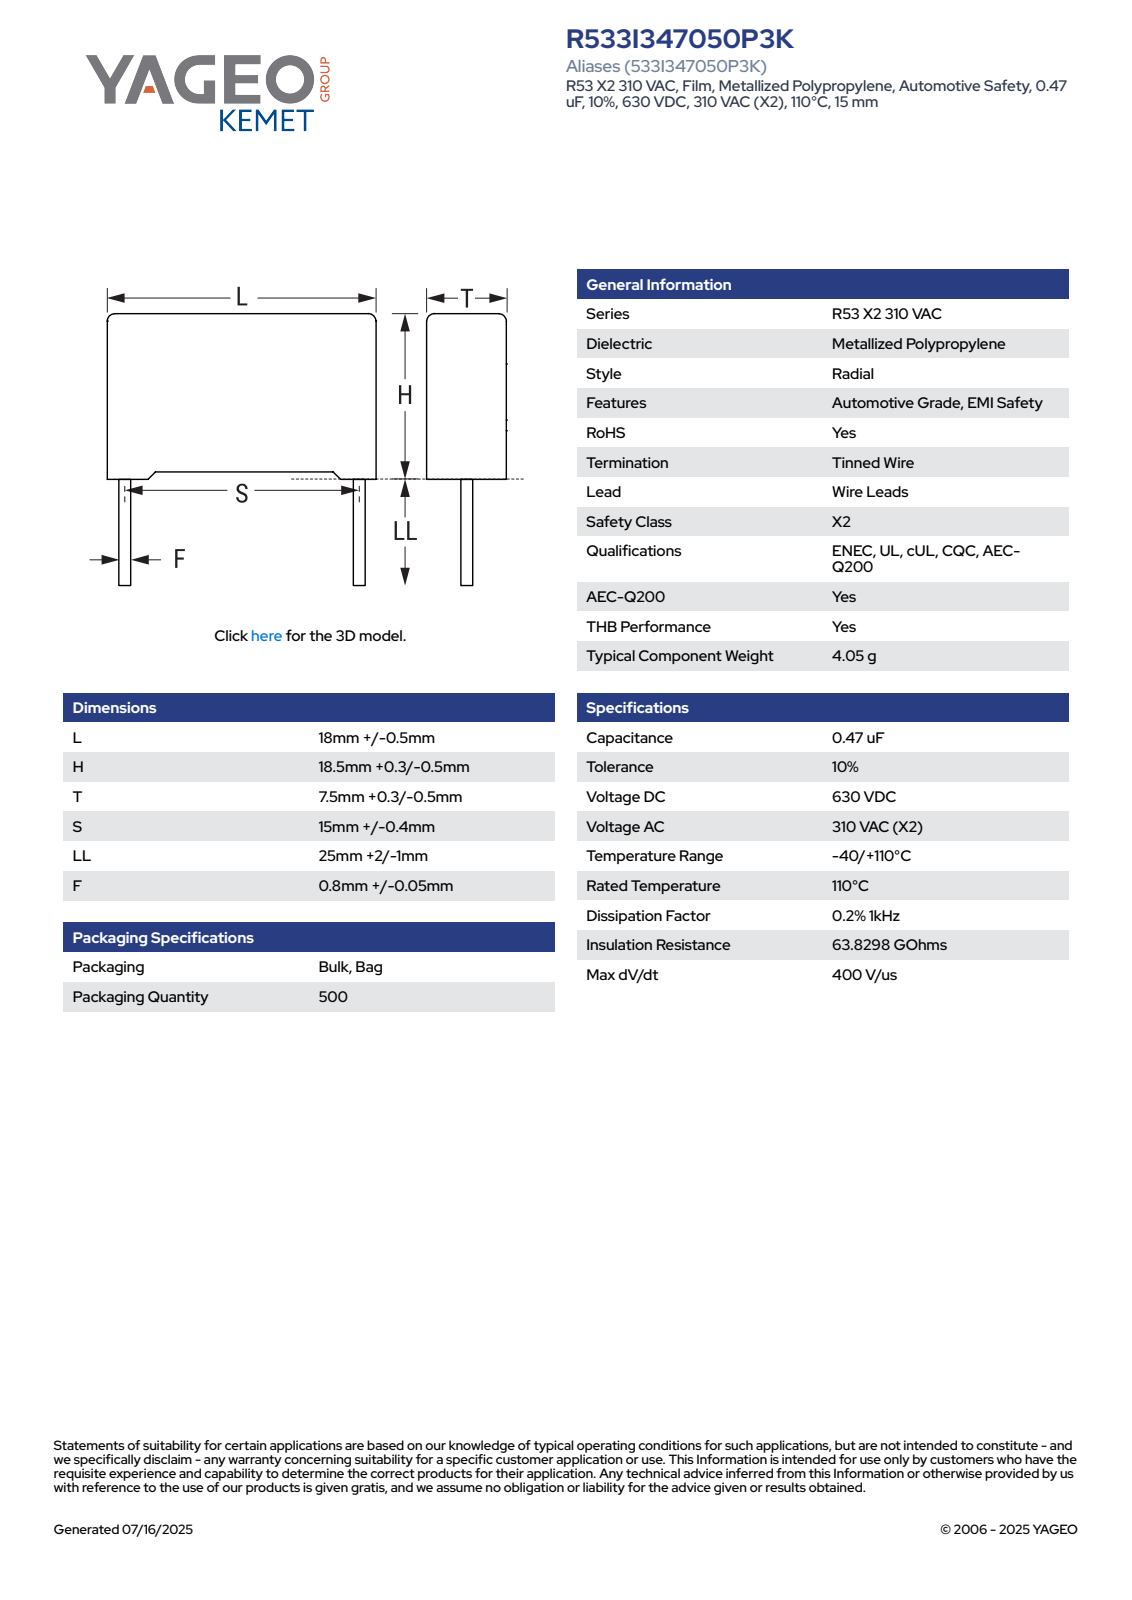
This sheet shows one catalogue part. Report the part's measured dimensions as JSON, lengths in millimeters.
{"part_name": "CFR_RB2_18X18.5X7.5_L18.5H18.8T7.8S15LL27F0.85", "step_written_by": "SolidWorks 2021 (AUTOMOTIVE_DESIGN)", "units": "millimeters", "bodies": {"solids": 4, "faces": 85, "planar": 77, "cylindrical": 8, "other": 0}, "overall_size": [45.8, 18.5, 7.8], "volume_mm3": 2647, "surface_area_mm2": 1447, "round_bosses_or_shafts": [[0.85, 2]], "partial_cylinders_radius": [[0.5, 4]], "face_to_face_distances": [7.8, 18.5, 18.05, 0.62, 0.75, 18.8, 0.65, 18.15, 7.18, 17.88]}
